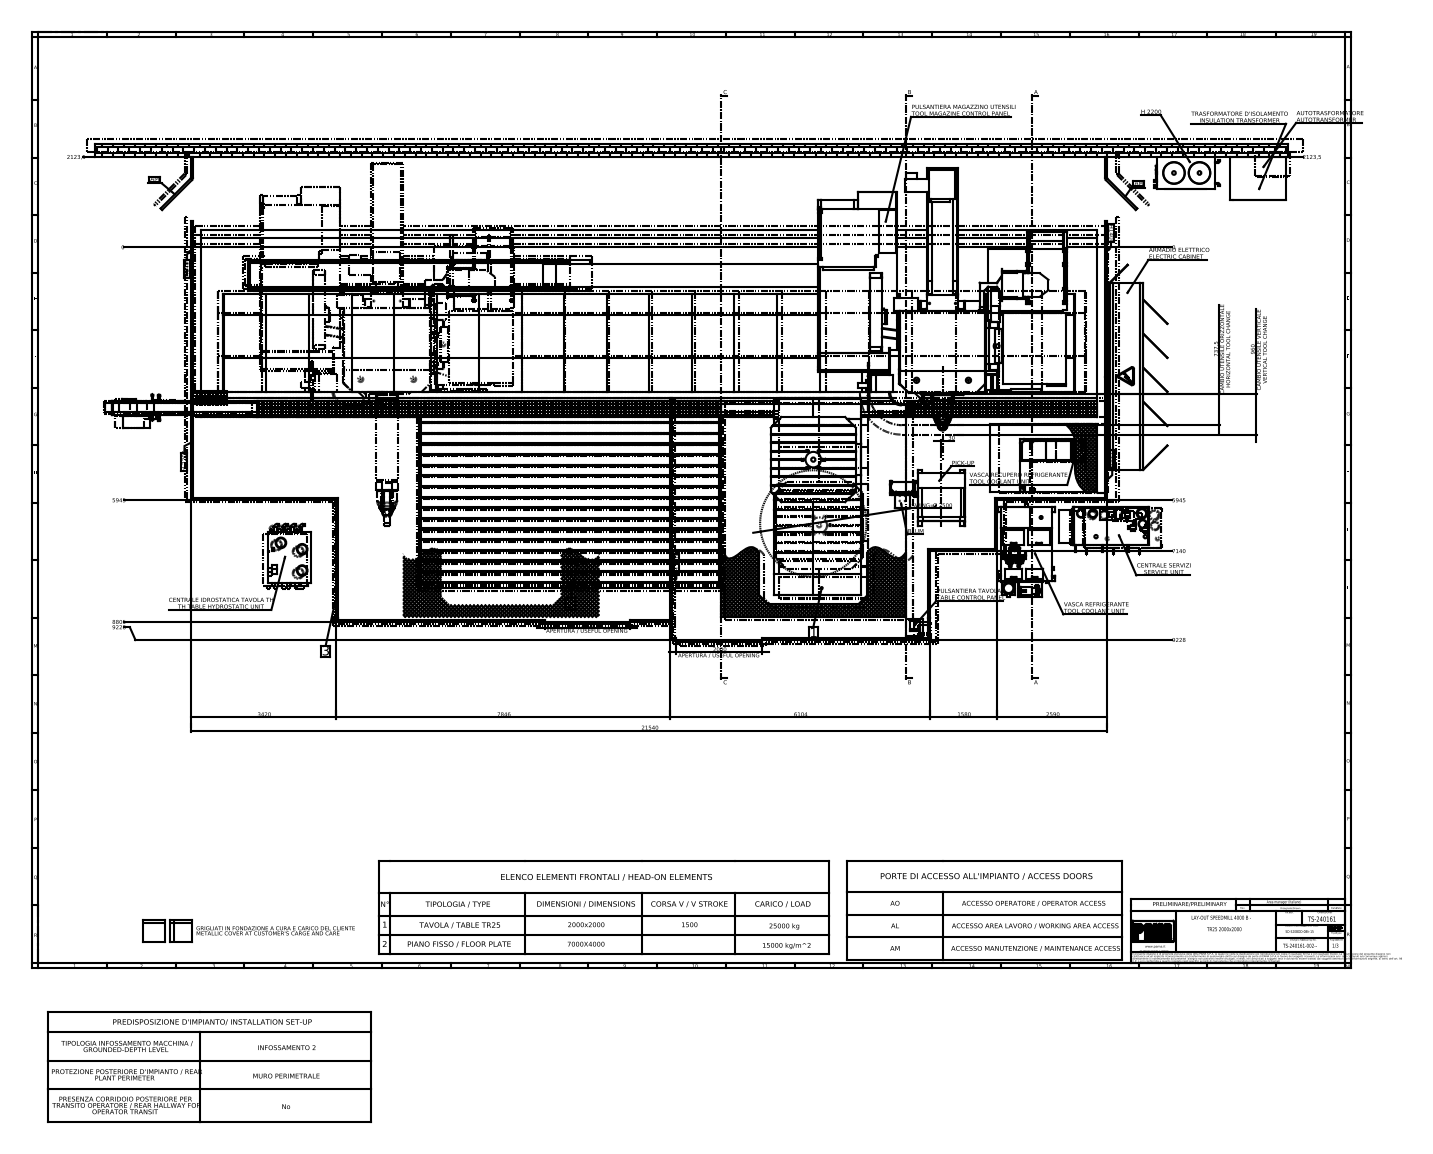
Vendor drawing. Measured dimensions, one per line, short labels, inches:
name: S003527; S002481_ANTE APERTE; S002835_X=13000; S000047 (+8 more)
written by: SolidWorks 2023 (AUTOMOTIVE_DESIGN)
unit: in
bodies: 491 solids, 7397 faces (5515 planar, 1443 cylindrical, 439 other)
size: 1103.937 × 574.862 × 370.079
volume: 51 440 000 in³; area: 4 325 000 in²
holes: 144× ⌀1.378, 123× ⌀2.74, 6× ⌀0.315, 6× ⌀1.26, 5× ⌀13.386, 4× ⌀0.551, 3× ⌀1.969, 2× ⌀0.165, 2× ⌀0.402, 2× ⌀0.748, 2× ⌀3.189, 2× ⌀3.346
bosses: 10× ⌀2.362, 8× ⌀2.165, 8× ⌀1.181, 6× ⌀5.906, 6× ⌀1.378, 5× ⌀7.874, 5× ⌀4.724, 4× ⌀14.893
rounds: 123× R0.197, 67× R0.591, 60× R1.378, 36× R0.236, 23× R0.394, 14× R0.945, 13× R0.079, 12× R0.984
face distances: 78.74, 11.811, 1.969, 52.756, 25.984, 574.862, 563.051, 3.15, 22.835, 76.772
hole spacings: 9.843, 19.685, 29.528, 39.37, 49.213, 59.055, 68.898, 78.74
